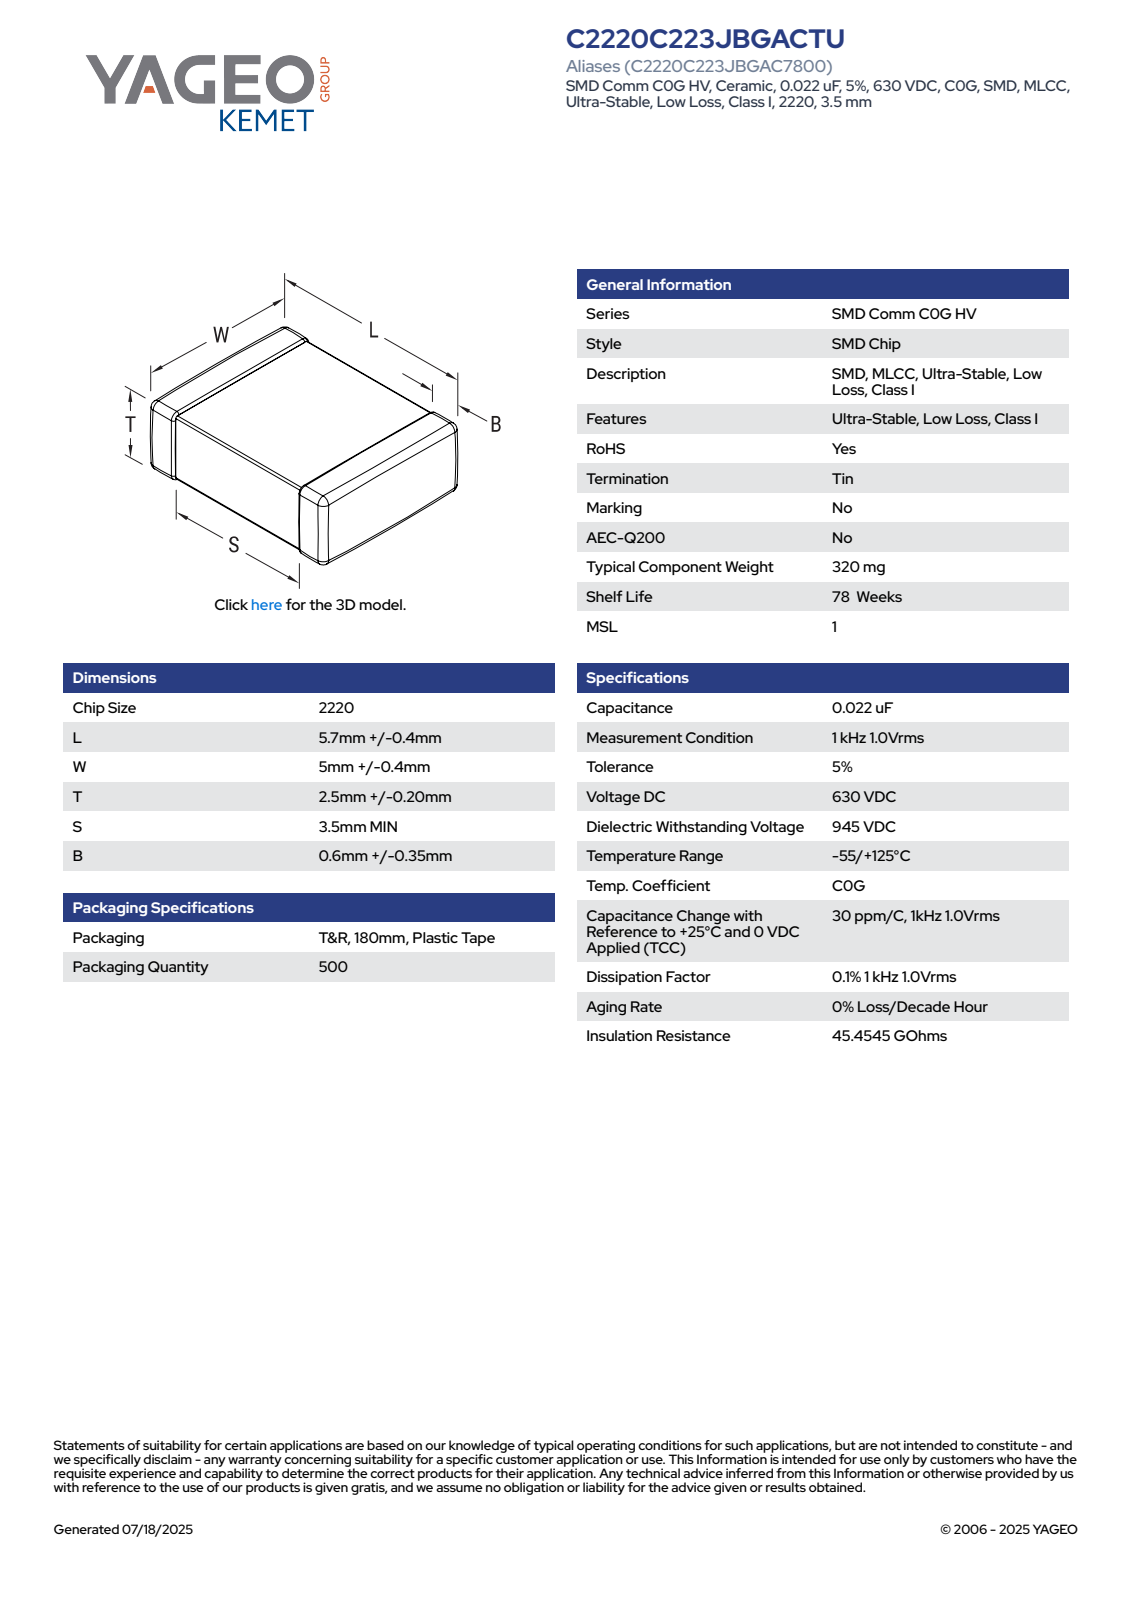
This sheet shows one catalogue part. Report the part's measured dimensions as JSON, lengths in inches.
{"part_name": "CCS_CCSTDNOS_2220_L6.1W5.4T2.7B0.95", "step_written_by": "SolidWorks 2014 (AUTOMOTIVE_DESIGN)", "units": "inches", "bodies": {"solids": 4, "faces": 125, "planar": 71, "cylindrical": 38, "other": 16}, "overall_size": [0.24, 0.213, 0.106], "volume_in3": 0.005, "surface_area_in2": 0.194, "partial_cylinders_radius": [[0.004, 24]], "face_to_face_distances": [0.098, 0.102, 0.24, 0.204, 0.106, 0.208, 0.213, 0.105, 0.108, 0.1]}
